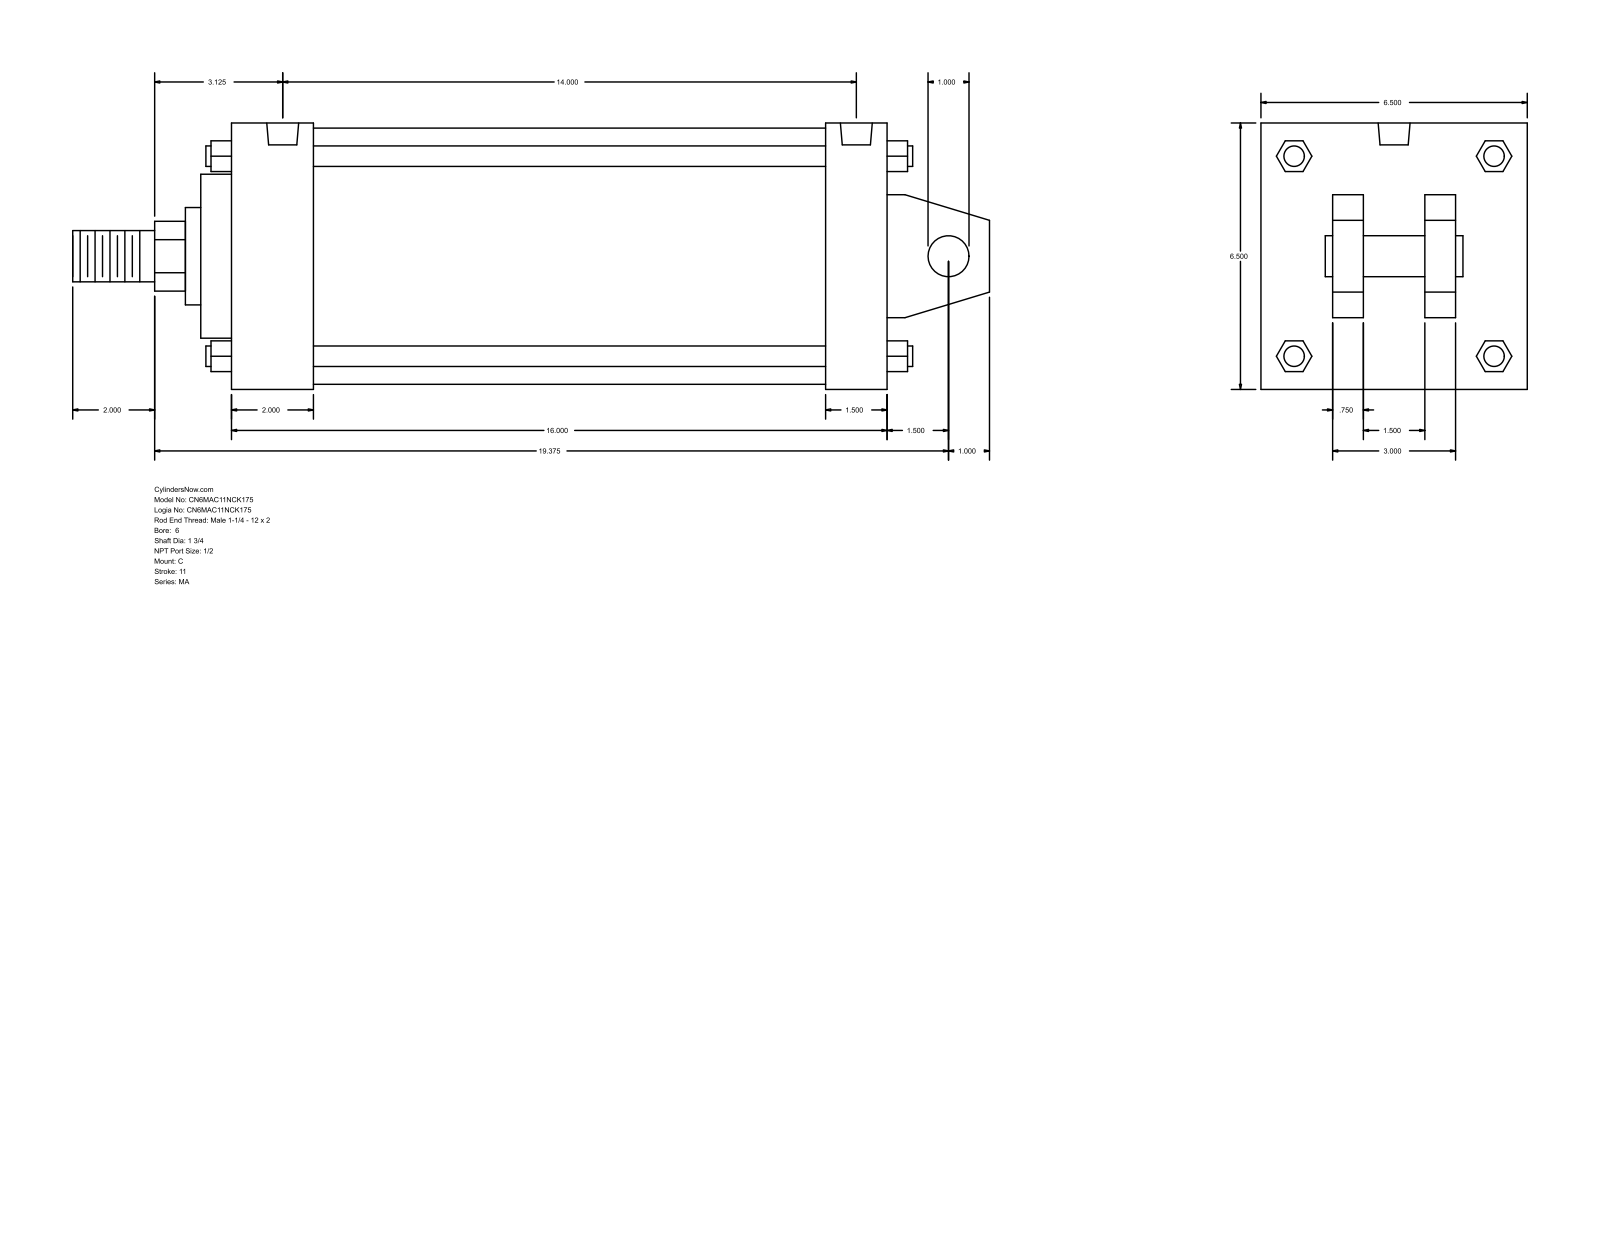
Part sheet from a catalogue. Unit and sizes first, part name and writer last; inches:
Units: inches
Overall size (bounding box): 22.375 × 6.5 × 6.5
Round holes (diameter × count): ⌀0.687 ×4, ⌀0.778 ×2
Round bosses / shafts (diameter × count): ⌀0.5 ×4, ⌀6.25 ×1, ⌀4 ×1, ⌀2.375 ×1, ⌀1.75 ×1, ⌀1.25 ×1, ⌀1 ×1
Partial cylindrical surfaces — rounded edges, fillets, slot ends (radius × count): R0.852 ×1
Main face-to-face distances: 6.5, 16, 0.75, 2.5, 4, 2, 4.75, 1.75, 14.5, 2.25
Hole centre spacings: 14
Bodies: 0 solids, 141 faces (109 planar, 32 cylindrical, 0 other)
Part name (STEP PRODUCT): MA_C__0600_1.75
STEP written by: GSSL Pune (CONFIG_CONTROL_DESIGN)
